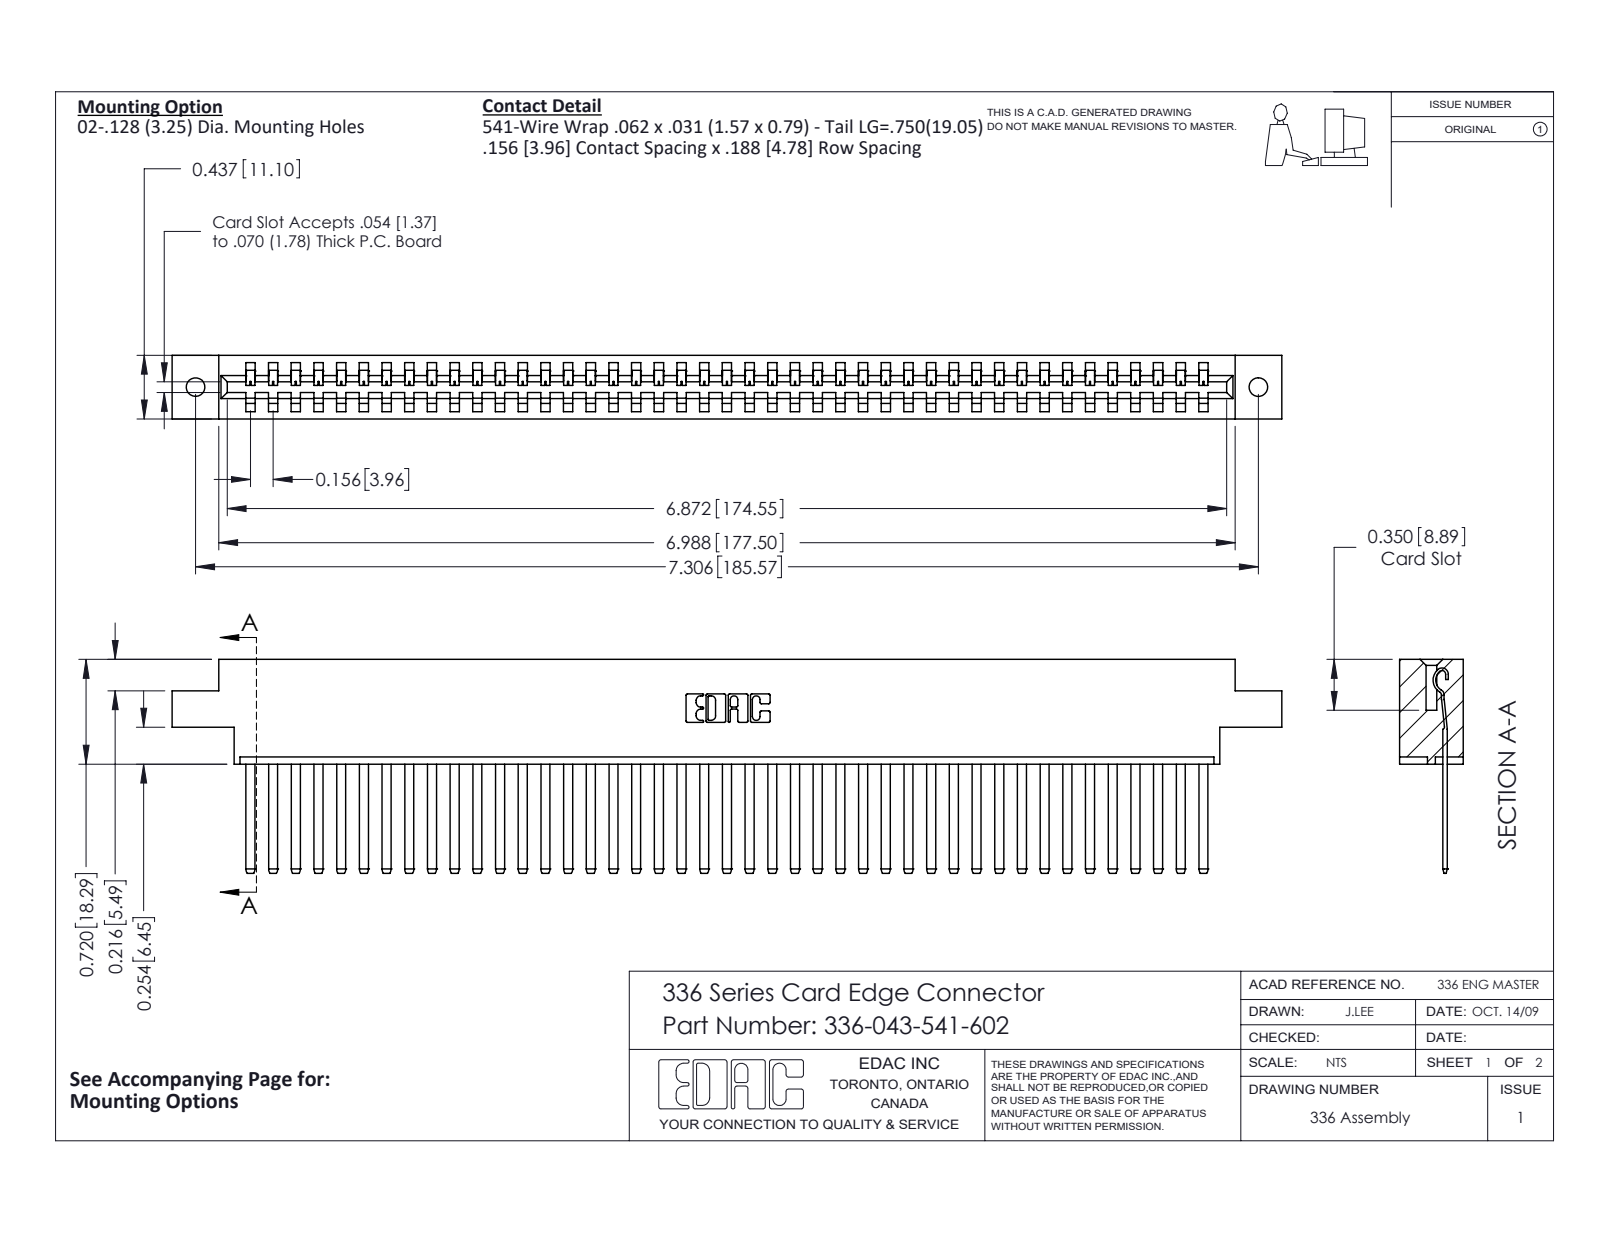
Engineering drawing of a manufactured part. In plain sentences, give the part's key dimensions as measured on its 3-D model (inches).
The part is named "336-043-541-602; 336 Part_Offset - .128 Dia; 336-290-001_336-290-541". Its 3-D file was written by "SolidWorks 2020 (CONFIG_CONTROL_DESIGN)". It is 44 solids with 2268 faces: 1536 planar, 732 cylindrical and 0 other. Overall it measures 7.629 by 1.47 by 0.437 inches. Its volume is 1.714 cubic inches and its surface area 47.27 square inches. Round holes: 2 of diameter 0.128. Partial cylindrical surfaces (rounded edges, fillets, slot ends): 86 of radius 0.004, 86 of radius 0.056, 22 of radius 0.01, 6 of radius 0.007, 6 of radius 0.031, 3 of radius 0.026, 2 of radius 0.022, 2 of radius 0.04. The main face-to-face distances are 0.437, 0.181, 0.328, 0.14, 0.297, 0.109, 0.031, 0.256, 0.05, 0.387. The hole center spacings are 7.306.
